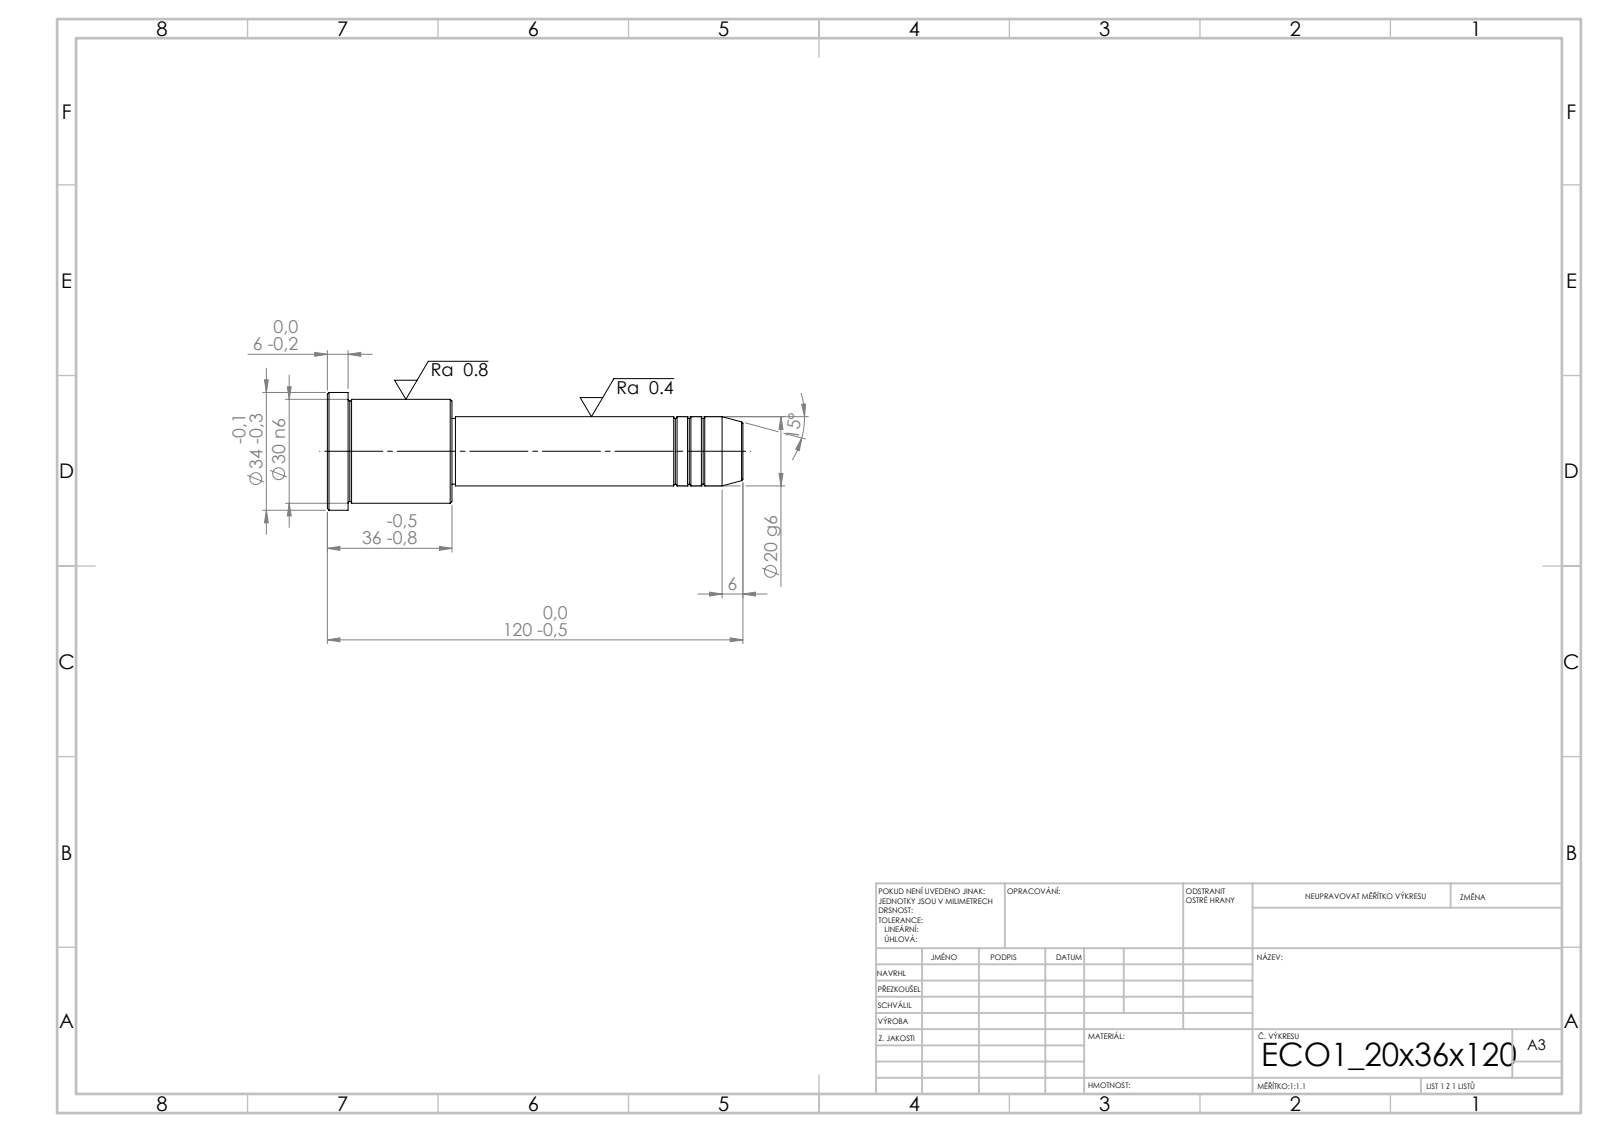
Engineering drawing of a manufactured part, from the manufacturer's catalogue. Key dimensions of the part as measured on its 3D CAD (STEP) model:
STEP written by: SolidWorks 2019 (CONFIG_CONTROL_DESIGN)
Units: millimetres
Bodies: 1 solid, 43 faces (5 planar, 14 cylindrical, 24 other)
Overall size (bounding box): 120 × 34 × 34
Volume: 52 590 mm³ · Surface area: 10 592 mm²
Round bosses / shafts (diameter × count): ⌀34 ×1, ⌀30 ×1, ⌀20 ×1, ⌀19 ×1
Main face-to-face distances: 36, 84, 120, 114, 30, 6, 83, 1, 31, 37
